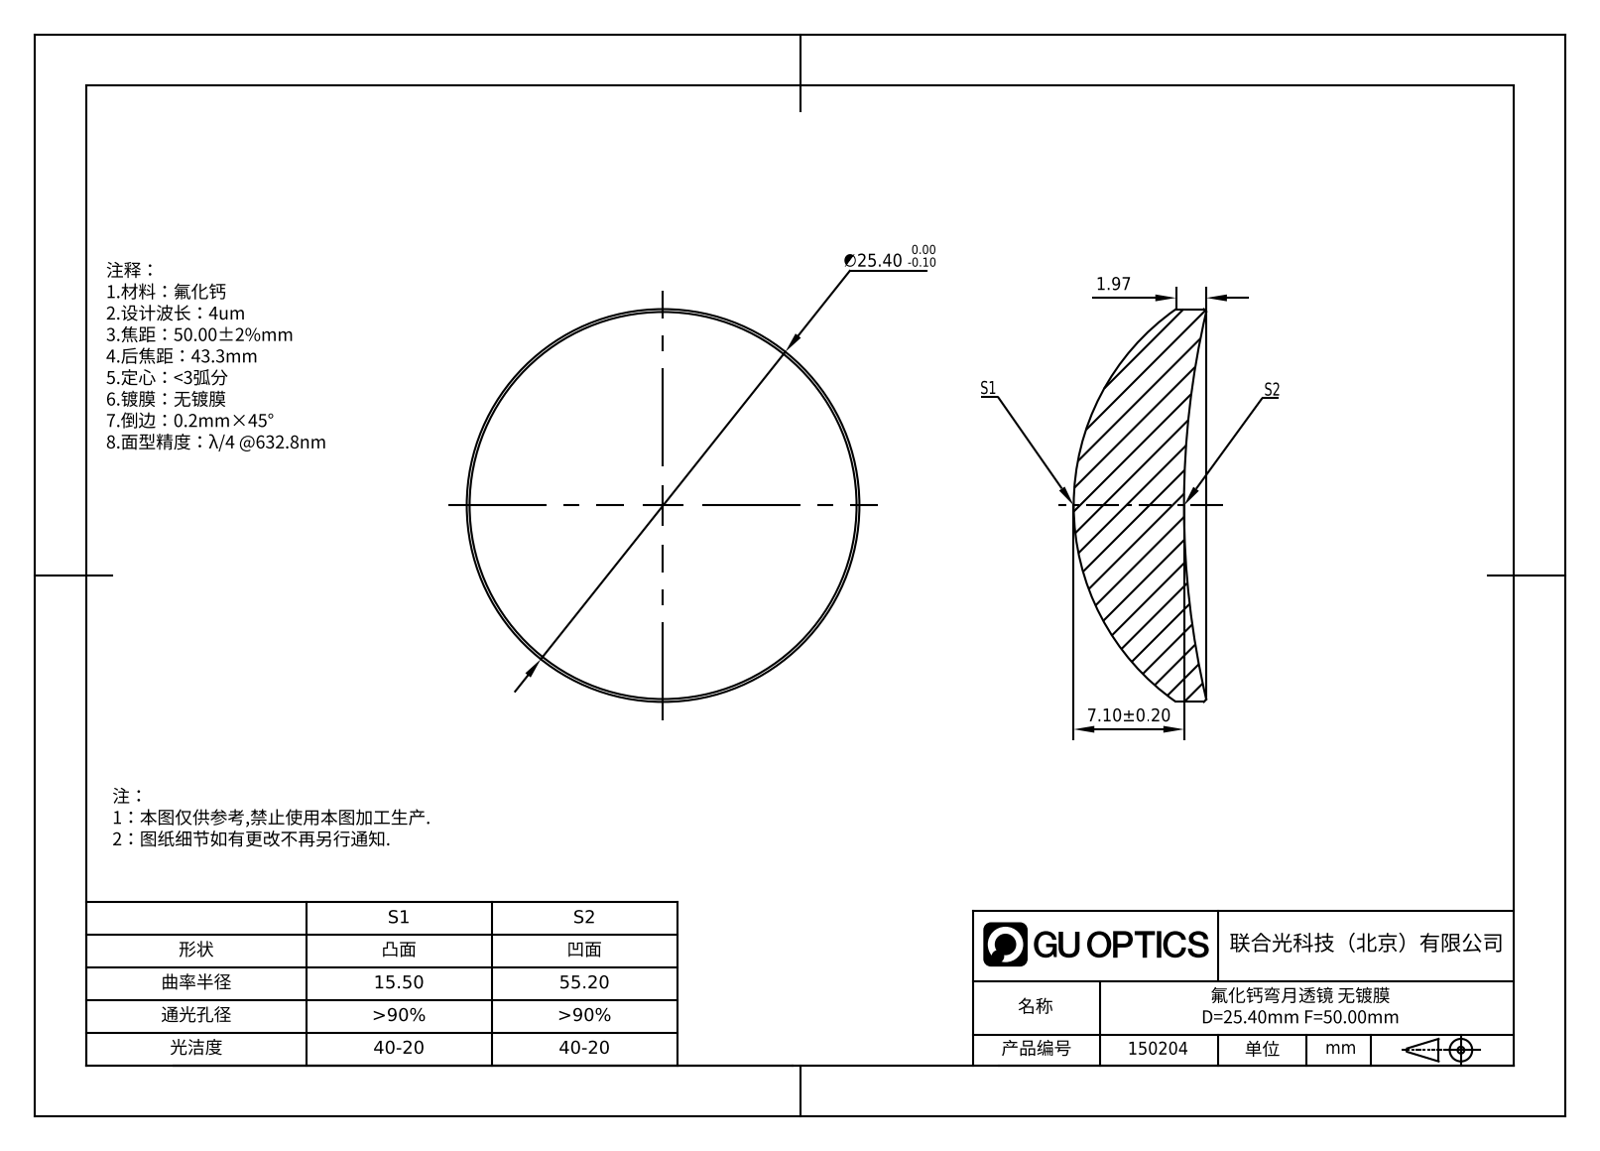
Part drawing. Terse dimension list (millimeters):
name: GLM5-025B-050
written by: SolidWorks 2022 (AUTOMOTIVE_DESIGN)
unit: mm
bodies: 1 solid, 8 faces (0 planar, 2 cylindrical, 6 other)
size: 25.4 × 25.4 × 8.58
volume: 2 462 mm³; area: 1 306 mm²
bosses: 1× ⌀25.4
